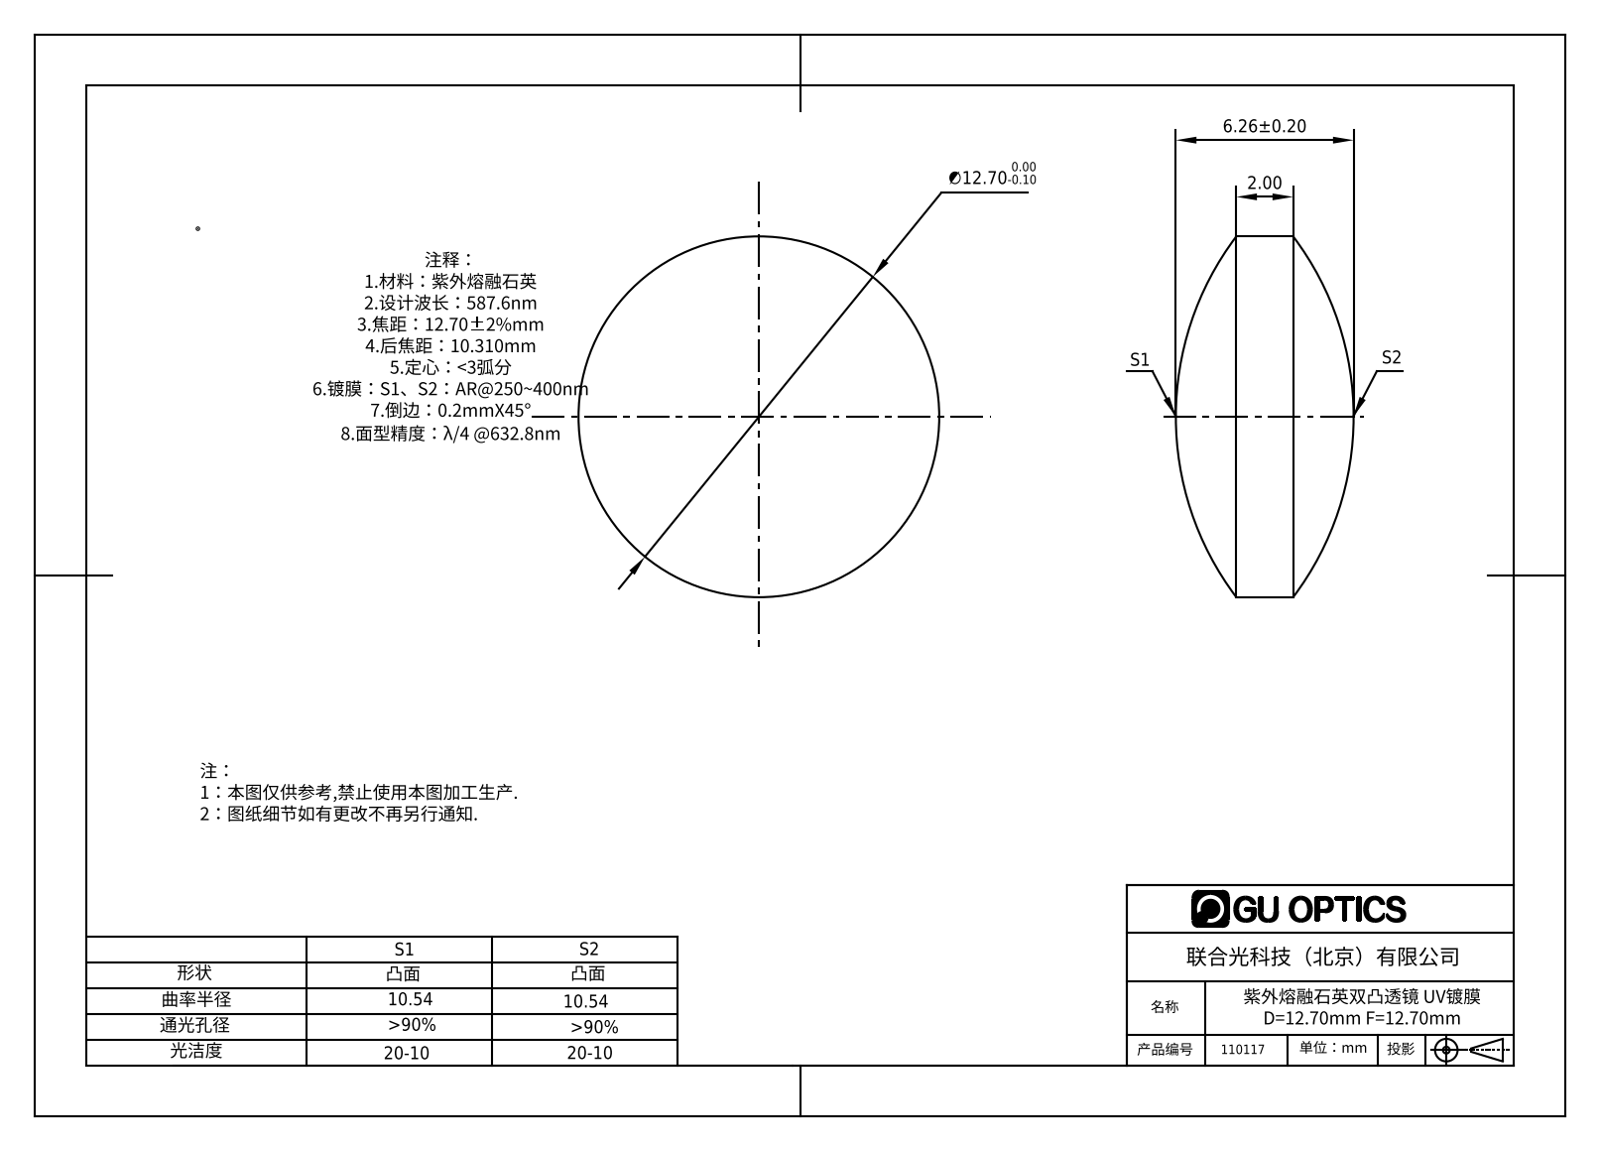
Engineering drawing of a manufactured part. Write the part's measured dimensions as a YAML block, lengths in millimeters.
part_name: "110093"
step_written_by: "SolidWorks 2016 (CONFIG_CONTROL_DESIGN)"
units: millimeters
bodies: {solids: 1, faces: 6, planar: 0, cylindrical: 2, other: 4}
overall_size: [12.7, 12.7, 6.26]
volume: 533
surface_area: 362
round_bosses_or_shafts:
  - {diameter: 12.7, count: 1}
